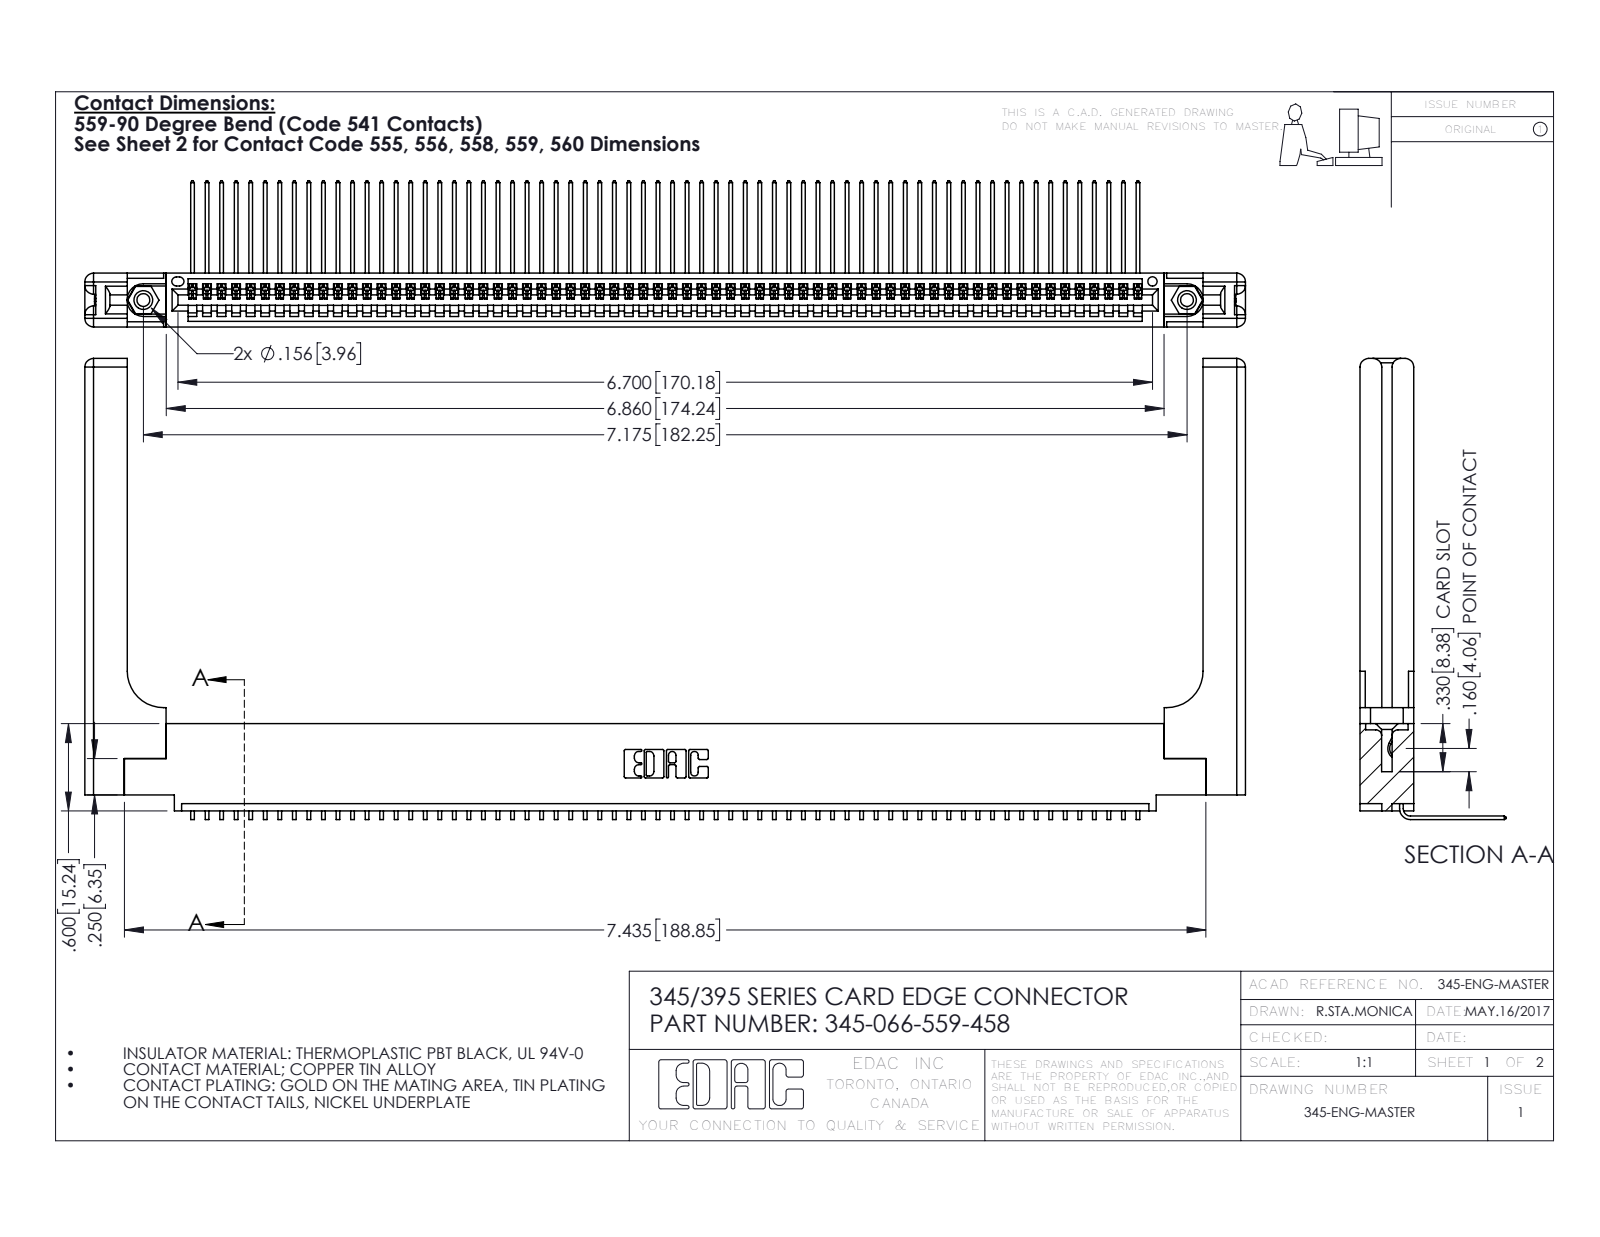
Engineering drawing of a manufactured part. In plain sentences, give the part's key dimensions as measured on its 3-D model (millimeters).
The part is named "345 Part_0.110 Offset - 0.156 Dia-TH; 345-066-559-458; 345-250-001_345-250-001-102; 345-292-001_558 559 Tail - 1 (+1 more)". Its 3-D file was written by "SolidWorks 2016 (CONFIG_CONTROL_DESIGN)". It is 71 solids with 4346 faces: 3004 planar, 1282 cylindrical and 60 other. Overall it measures 202.7 by 80.5 by 25.5 millimeters. Its volume is 28 100 cubic millimeters and its surface area 33 050 square millimeters. Round holes: 2 of diameter 2.3, 2 of diameter 3.2, 2 of diameter 4, 1 of diameter 1.6. Round bosses or shafts: 2 of diameter 3.9. Partial cylindrical surfaces (rounded edges, fillets, slot ends): 132 of radius 0.2, 22 of radius 0.3, 16 of radius 1.5, 6 of radius 0.2, 6 of radius 0.8, 3 of radius 0.7, 2 of radius 0.8, 2 of radius 0.8. The main face-to-face distances are 1.8, 9.4, 7.6, 2.5, 6.9, 0.6, 5.1, 5.7, 3.8, 3.8. The hole center spacings are 6.9, 176.3, 182.2.
